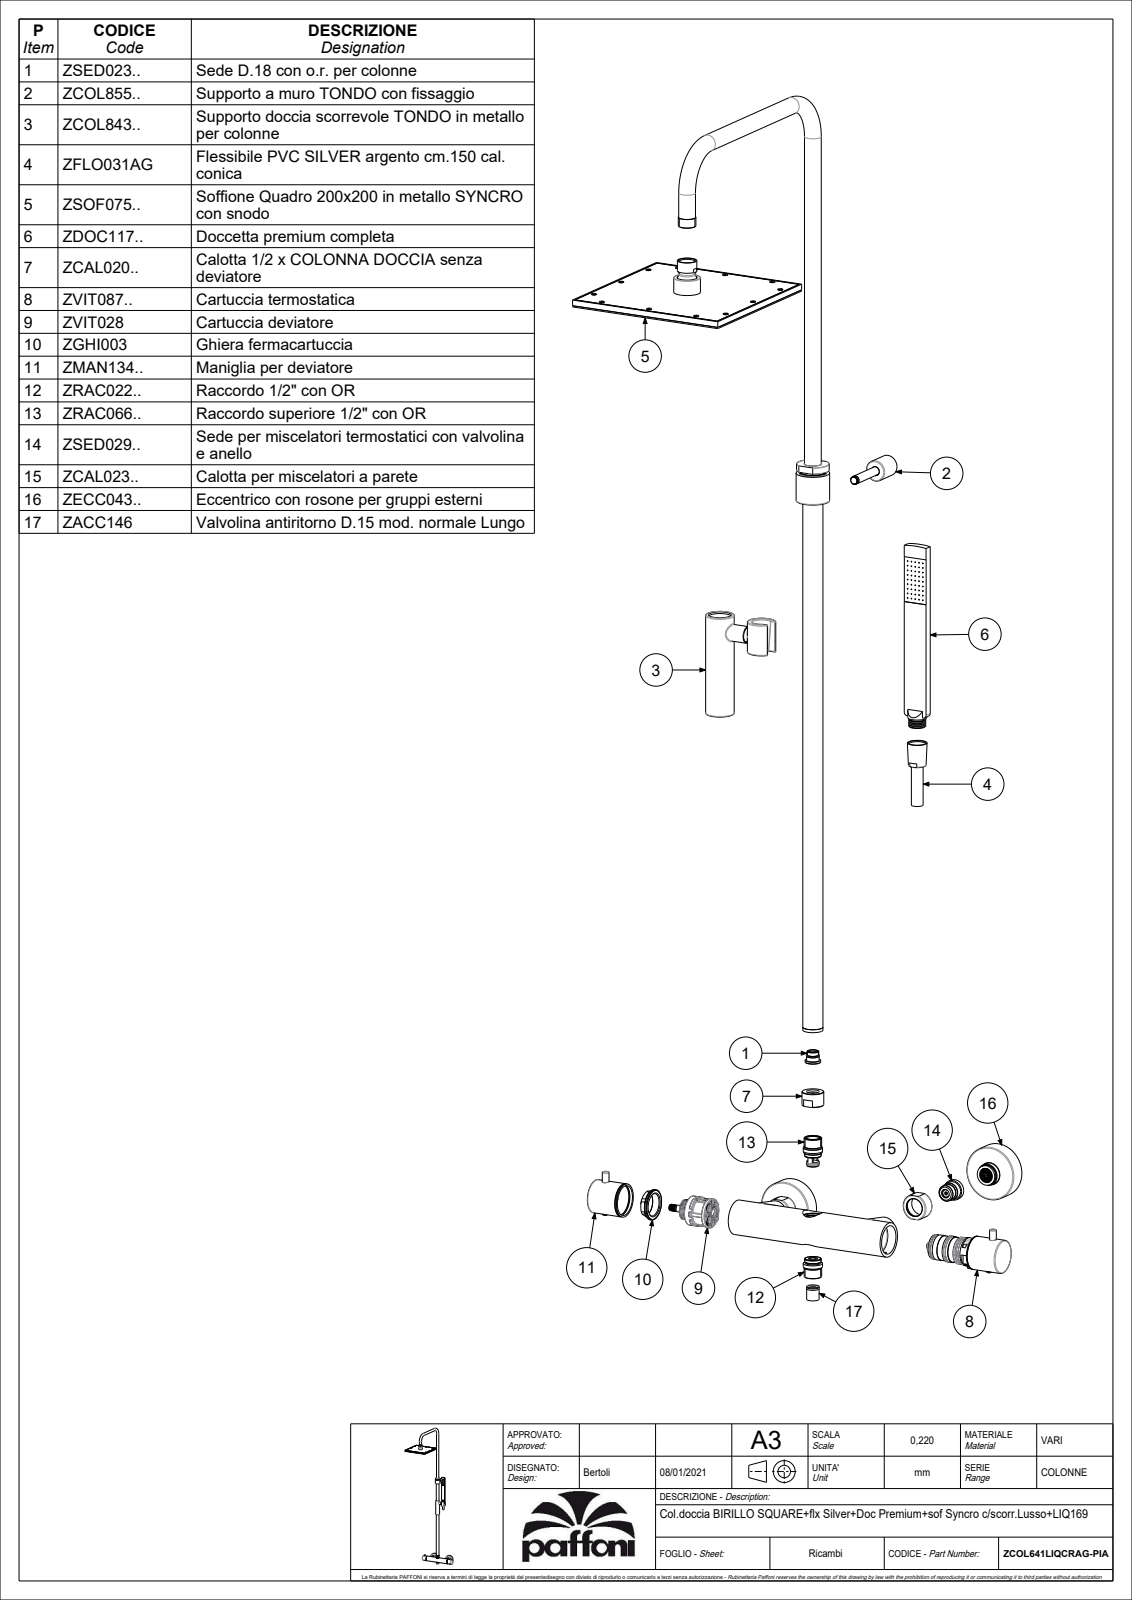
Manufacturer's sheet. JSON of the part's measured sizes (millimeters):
{"part_name": "ZCOL641LIQCRAG-PIA", "step_written_by": "CREO PARAMETRIC BY PTC INC, 2022124 (CONFIG_CONTROL_DESIGN)", "units": "millimeters", "bodies": {"solids": 10, "faces": 6615, "planar": 1228, "cylindrical": 1339, "other": 4048}, "overall_size": [1236.1, 482.8, 287.73], "volume_mm3": 753237, "surface_area_mm2": 598179, "round_holes": [[1.5, 100], [1.7, 100], [7, 16], [2.5, 14], [6, 14], [5.1, 12], [4, 4], [17, 4], [15.1, 3], [16, 3], [25, 3], [3, 2]], "round_bosses_or_shafts": [[10, 101], [5, 12], [2, 11], [20, 4], [40, 3], [24, 3], [8, 3], [64.5, 2]], "partial_cylinders_radius": [[1.5, 64], [0.3, 24], [1, 20], [20, 12], [1.75, 4], [4, 4], [12, 4], [6.5, 2]], "face_to_face_distances": [8.5, 1, 7.5, 7, 6, 1.5, 2.9, 1.4, 4.6, 5.6], "hole_center_spacings": [36.45, 16.3, 23.05, 32.6, 51.55, 67.21, 48.9, 83.11]}
